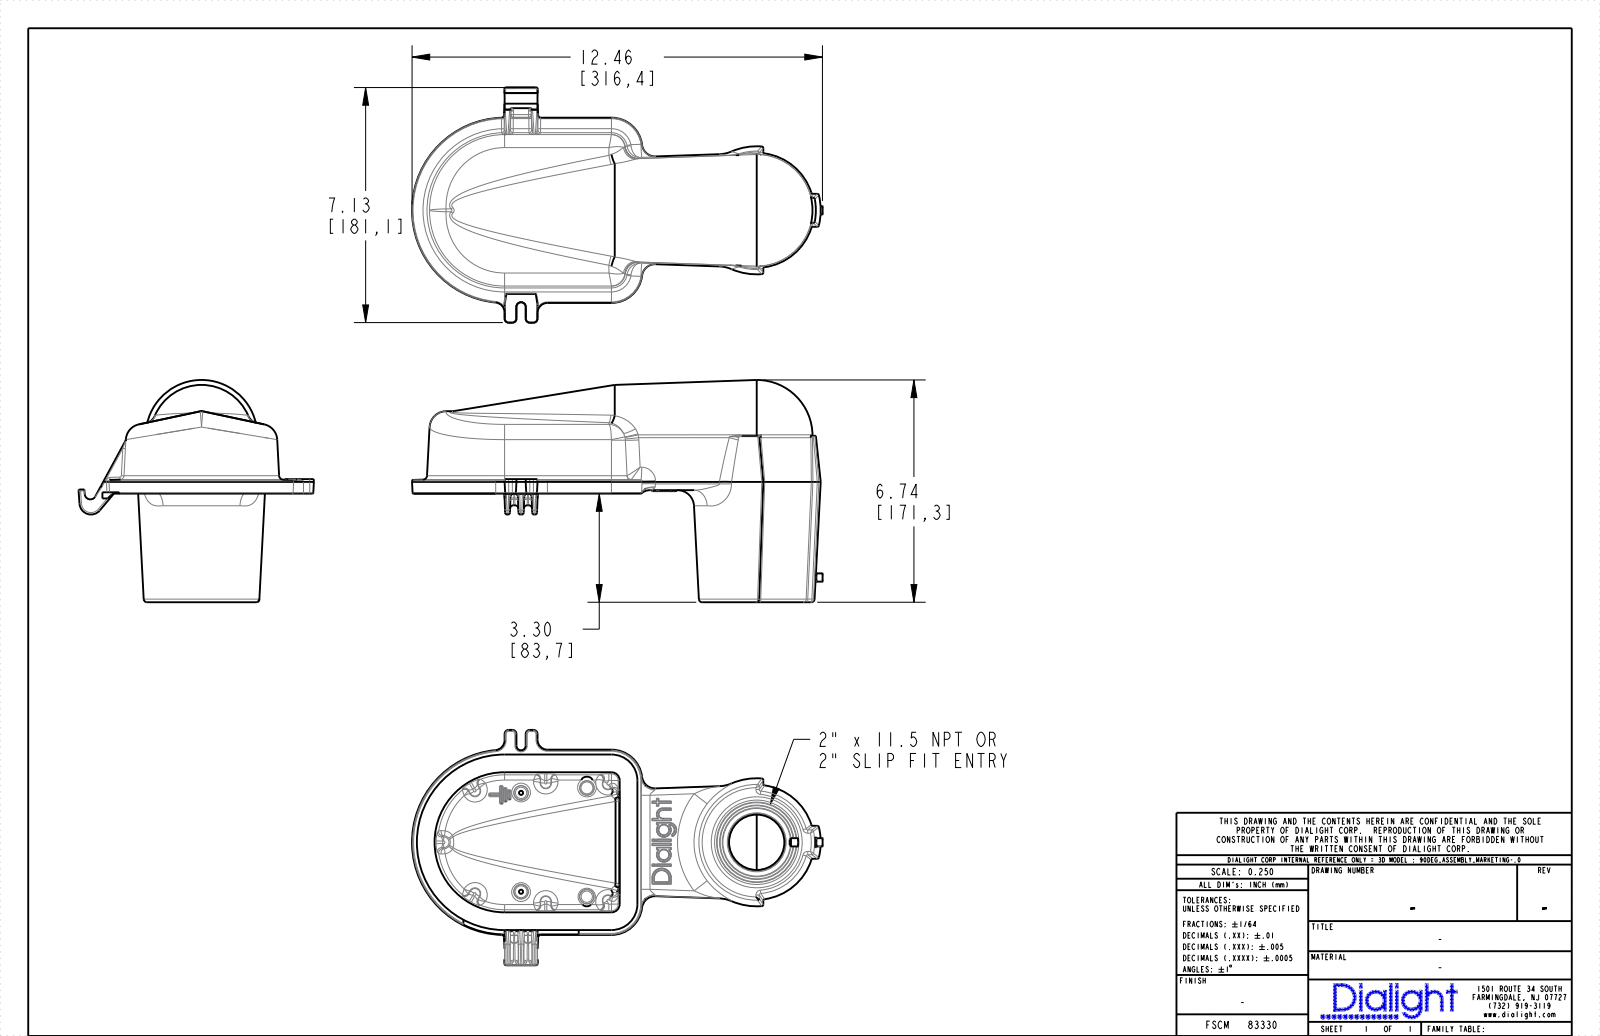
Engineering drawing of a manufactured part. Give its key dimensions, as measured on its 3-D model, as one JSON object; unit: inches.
{"part_name": "3098HZC201900; 6000HIB000901; 90DEG_ASSEMBLY_MARKETING_ASM", "step_written_by": "CREO PARAMETRIC BY PTC INC, 2021304 (CONFIG_CONTROL_DESIGN)", "units": "inches", "bodies": {"solids": 2, "faces": 1195, "planar": 225, "cylindrical": 366, "other": 604}, "overall_size": [12.464, 7.143, 6.743], "volume_in3": 56.36, "surface_area_in2": 322.3, "round_holes": [[0.125, 2], [0.257, 1]], "round_bosses_or_shafts": [[0.25, 1]], "partial_cylinders_radius": [[0.01, 107], [0.025, 46], [0.125, 20], [0.2, 19], [0.03, 18], [0.04, 15], [0.08, 14], [0.06, 12]], "face_to_face_distances": [0.25, 0.44, 0.25, 0.5, 0.165, 0.06, 0.605, 0.105, 3.9, 3.46], "hole_center_spacings": [3]}
